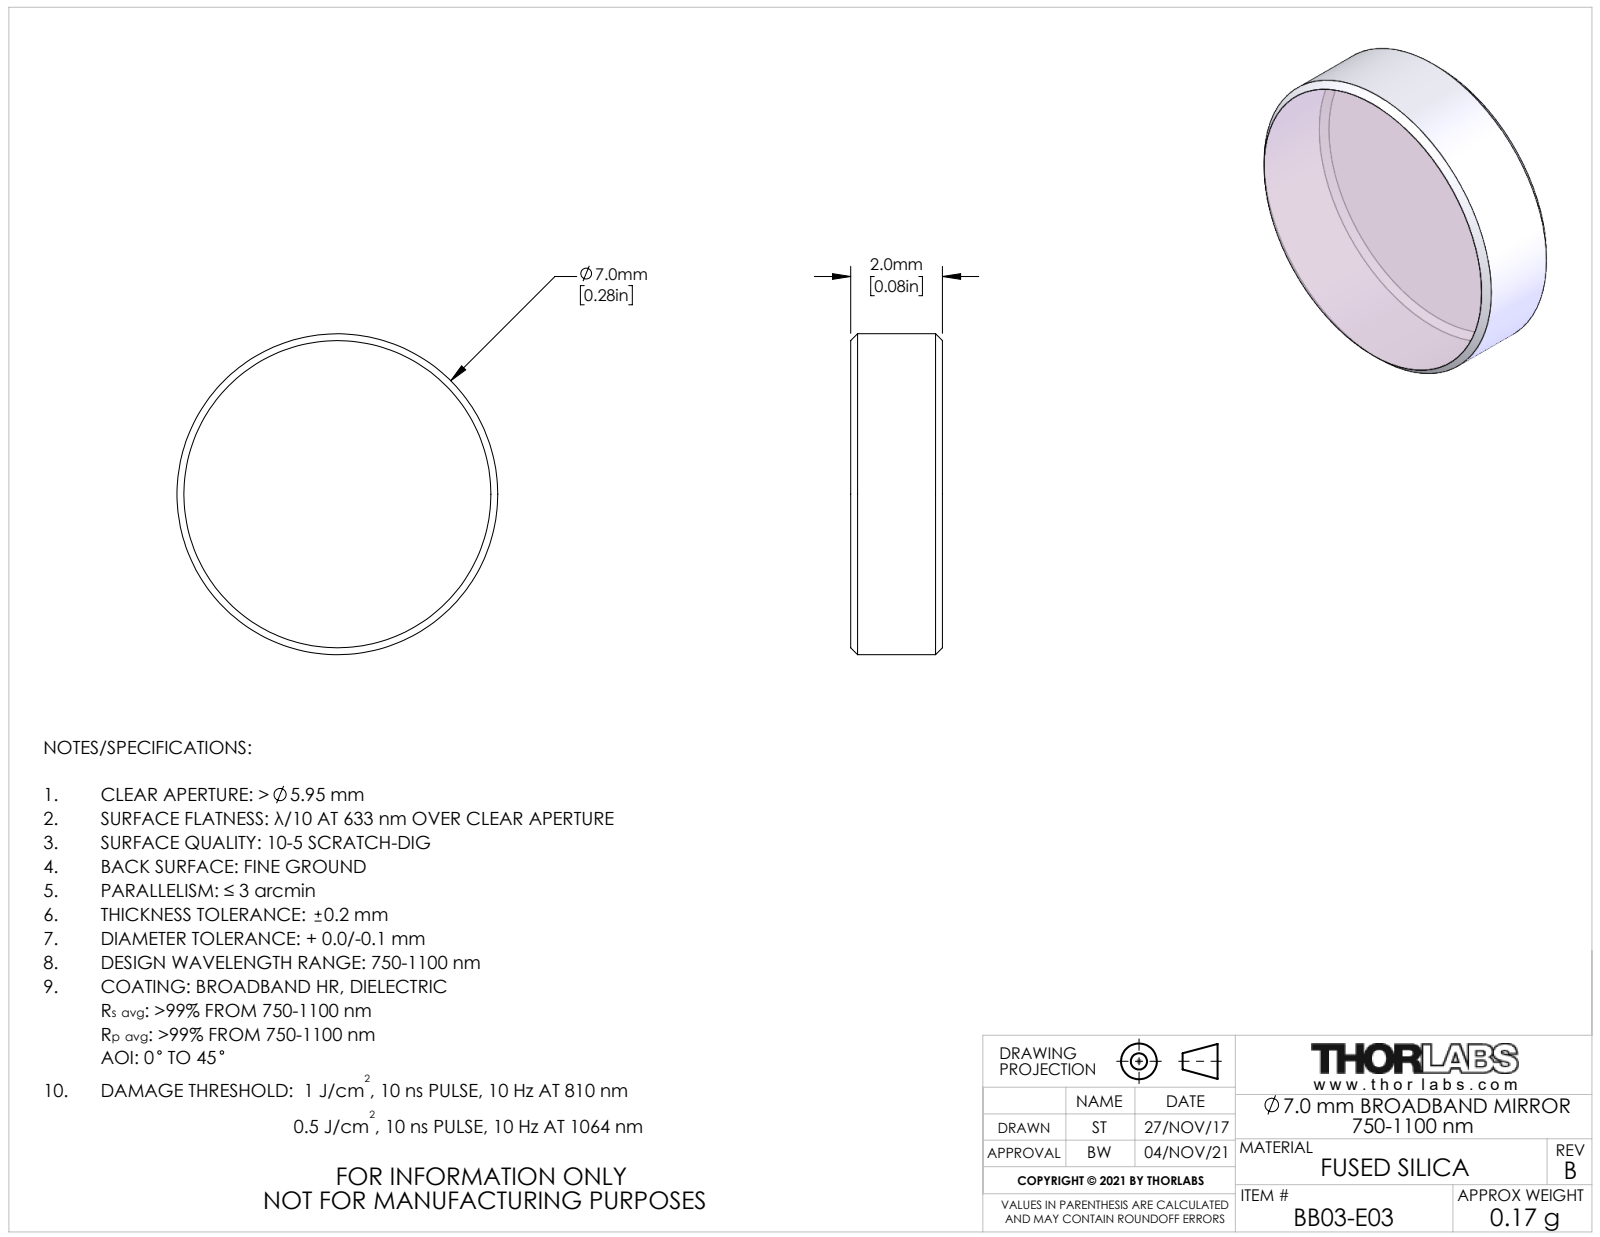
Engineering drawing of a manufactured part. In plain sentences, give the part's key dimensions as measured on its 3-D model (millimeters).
The part is named "TTN146933-E0W". Its 3-D file was written by "SolidWorks 2016 (CONFIG_CONTROL_DESIGN)". It is 1 solid with 8 faces: 2 planar, 2 cylindrical and 4 other. Overall it measures 7 by 7 by 2 millimeters. Its volume is 76 cubic millimeters and its surface area 117 square millimeters. Round bosses or shafts: 1 of diameter 7. The main face-to-face distances are 2.
